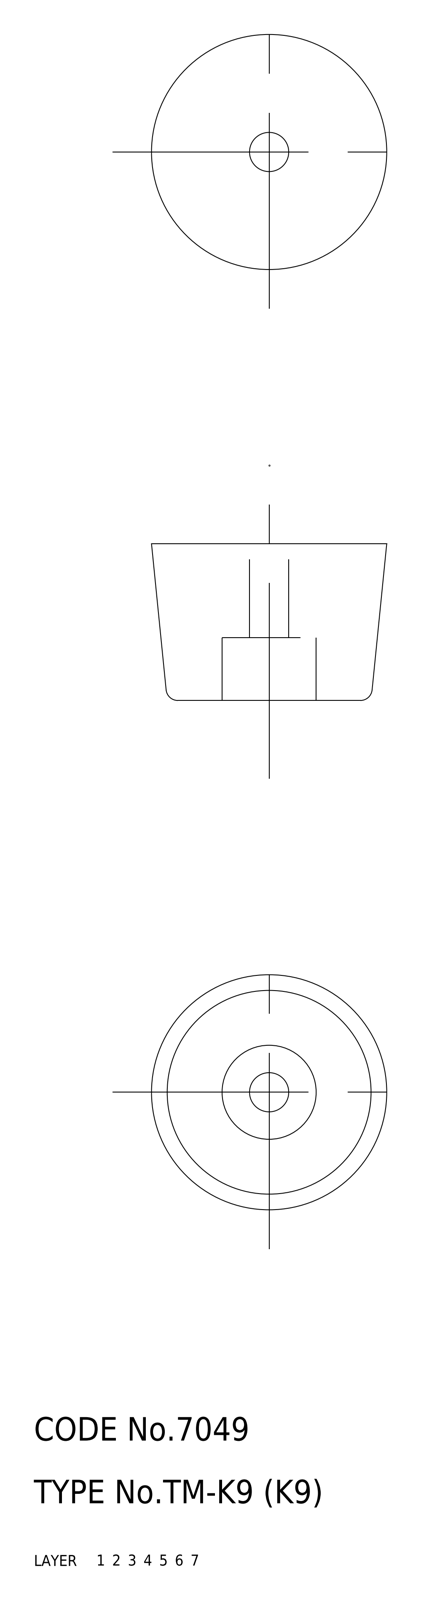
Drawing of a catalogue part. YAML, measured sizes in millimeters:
part_name: "rubber foot"
step_written_by: "CADfix (AUTOMOTIVE_DESIGN)"
units: millimeters
bodies: {solids: 1, faces: 11, planar: 0, cylindrical: 0, other: 11}
overall_size: [30, 30, 20]
volume: 11191
surface_area: 3416
